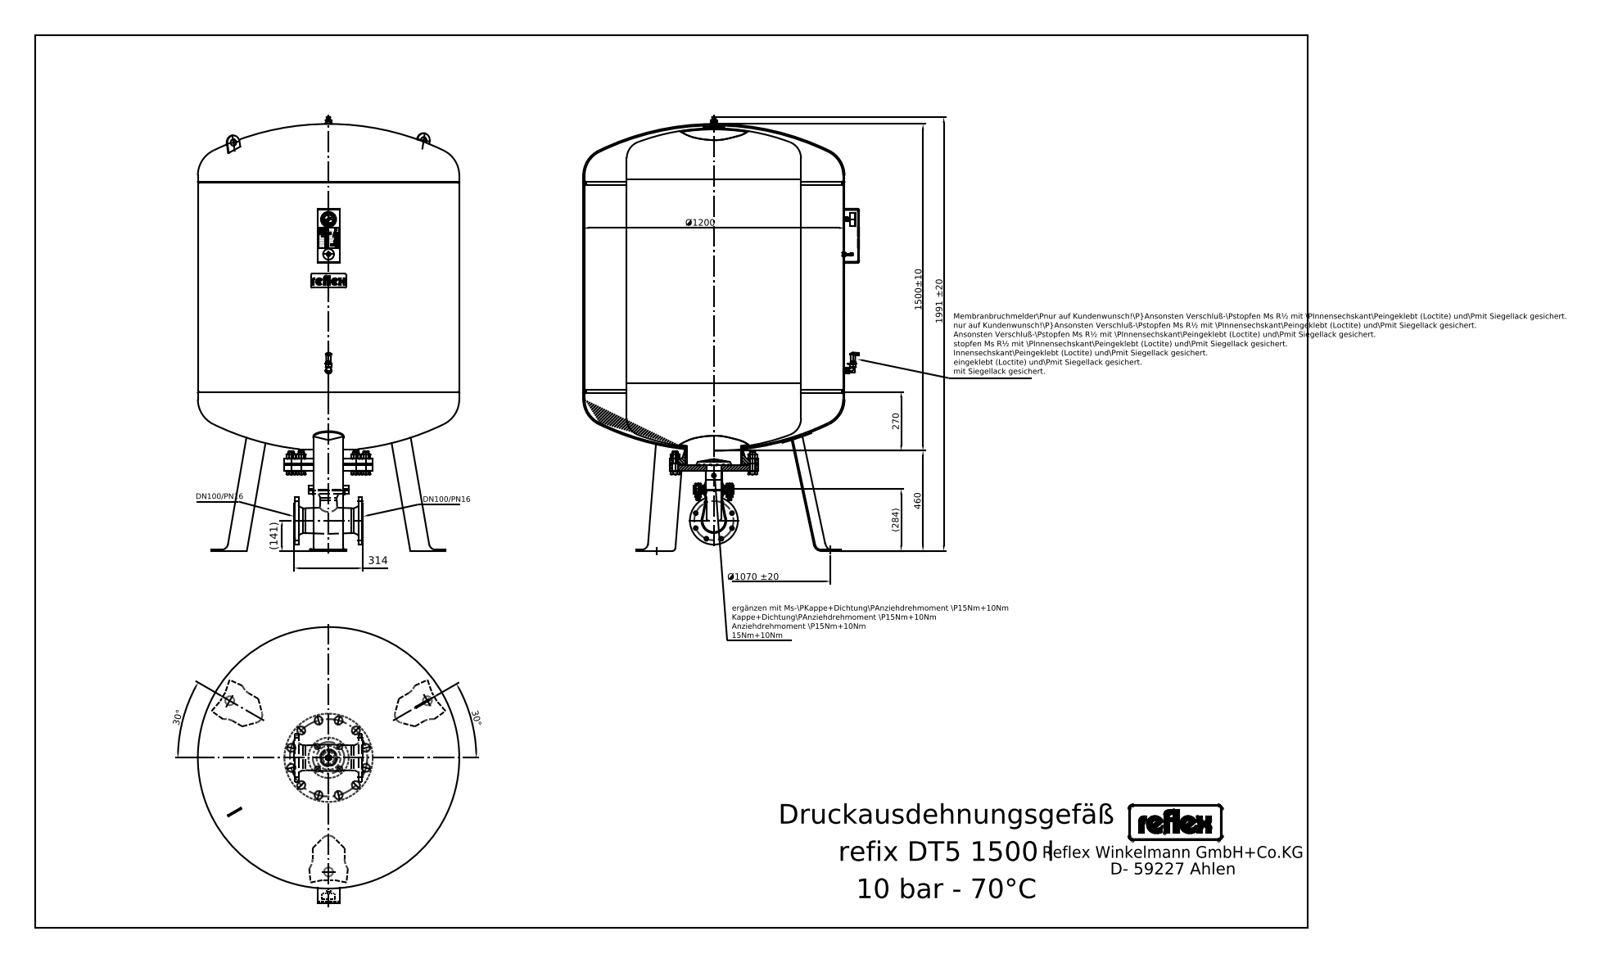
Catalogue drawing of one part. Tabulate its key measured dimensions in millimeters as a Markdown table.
| quantity | value |
| --- | --- |
| STEP written by | Mechanical Desktop 2008 (CONFIG_CONTROL_DESIGN) |
| units | millimeters |
| bodies | 31 solids, 795 faces (417 planar, 195 cylindrical, 183 other) |
| overall size | 2000 × 1266 × 1200 |
| volume | 1 539 000 000 mm³ |
| surface area | 13 450 000 mm² |
| round holes (diameter × count) | 19 × 8, 10 × 1, 30 × 1, 50 × 1, 69 × 1, 114.3 × 1, 260.4 × 1 |
| round bosses / shafts (diameter × count) | 16 × 17, 28 × 2, 26 × 2, 20 × 2, 1200 × 1, 405 × 1, 273 × 1, 220 × 1 |
| partial cylindrical surfaces (radius × count) | 25 × 18, 5.62 × 4, 2.25 × 3, 9 × 3, 1 × 2, 3.84 × 2, 5 × 2, 6.75 × 2 |
| main face-to-face distances | 1000, 26, 312, 1312, 338, 1338, 31, 5.97, 5.89, 281 |
| hole center spacings | 90, 127.28, 166.3, 68.88, 68.89, 180, 82.33, 615.5 |
